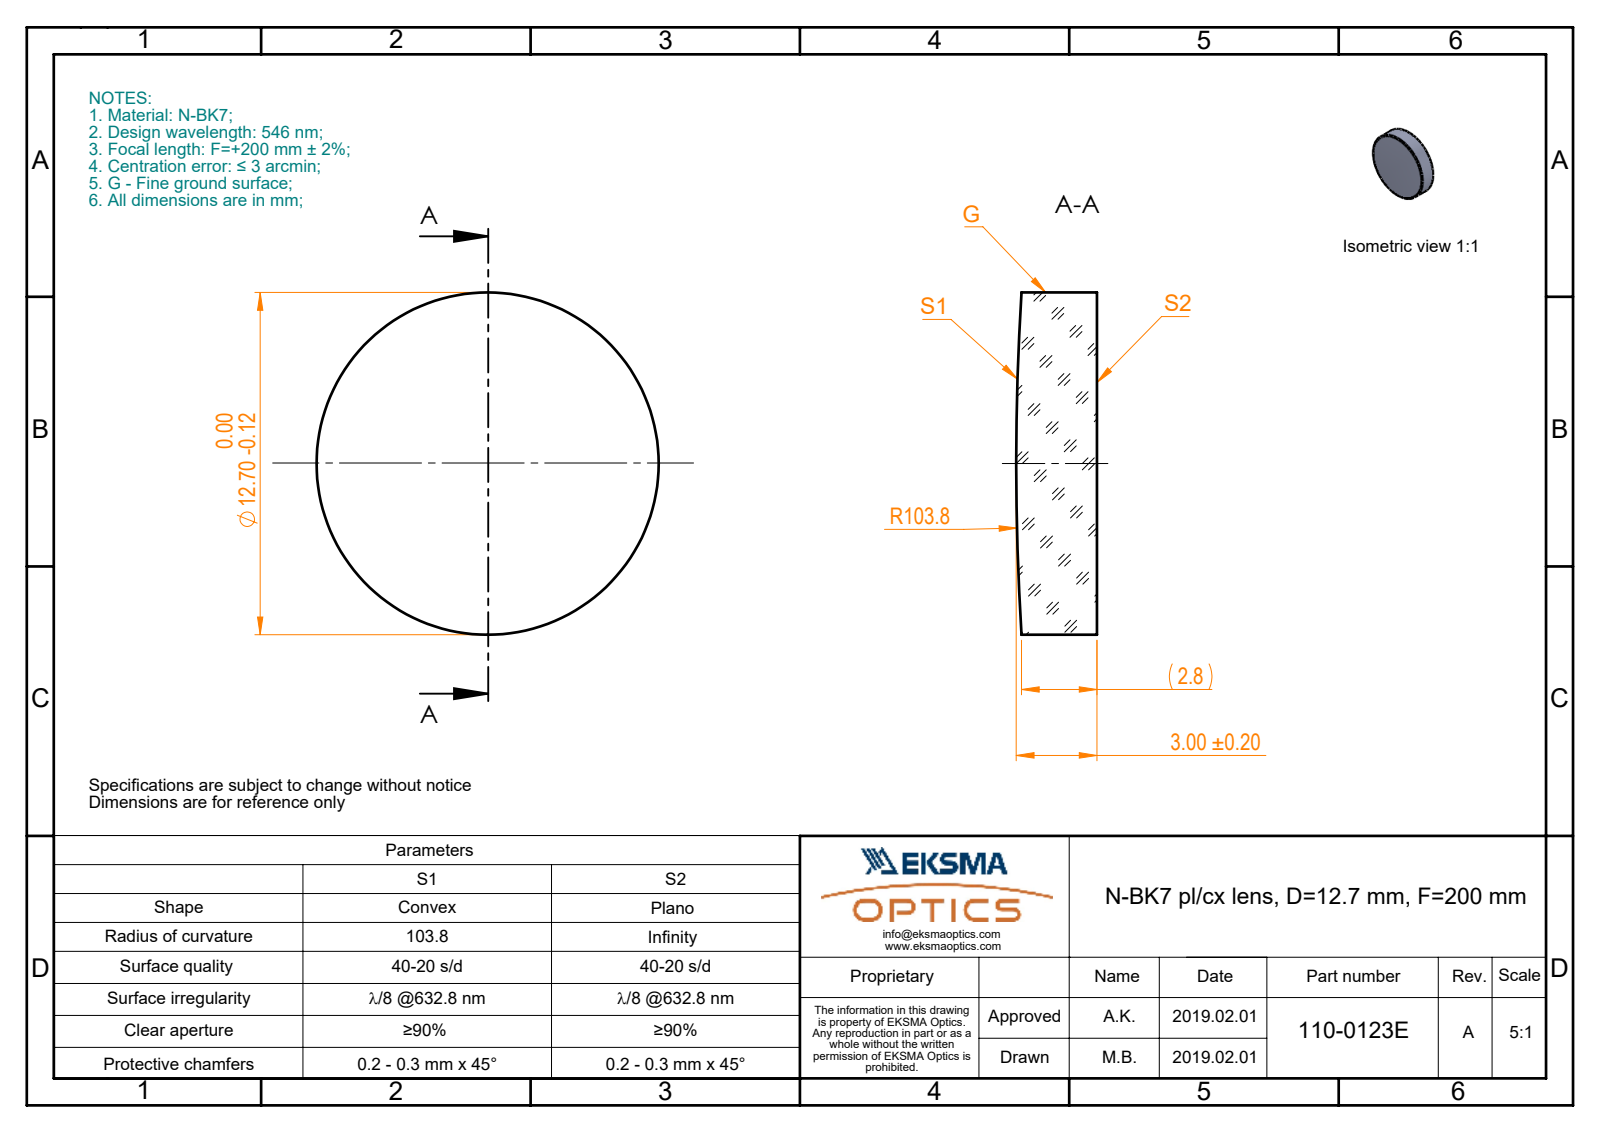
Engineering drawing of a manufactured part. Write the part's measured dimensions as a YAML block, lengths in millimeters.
part_name: "110-0123E BK7 pl-cx 12.7 F200"
step_written_by: "SolidWorks 2017 (CONFIG_CONTROL_DESIGN)"
units: millimeters
bodies: {solids: 1, faces: 5, planar: 1, cylindrical: 2, other: 2}
overall_size: [12.7, 12.7, 3]
volume: 368
surface_area: 365
round_bosses_or_shafts:
  - {diameter: 12.7, count: 1}
